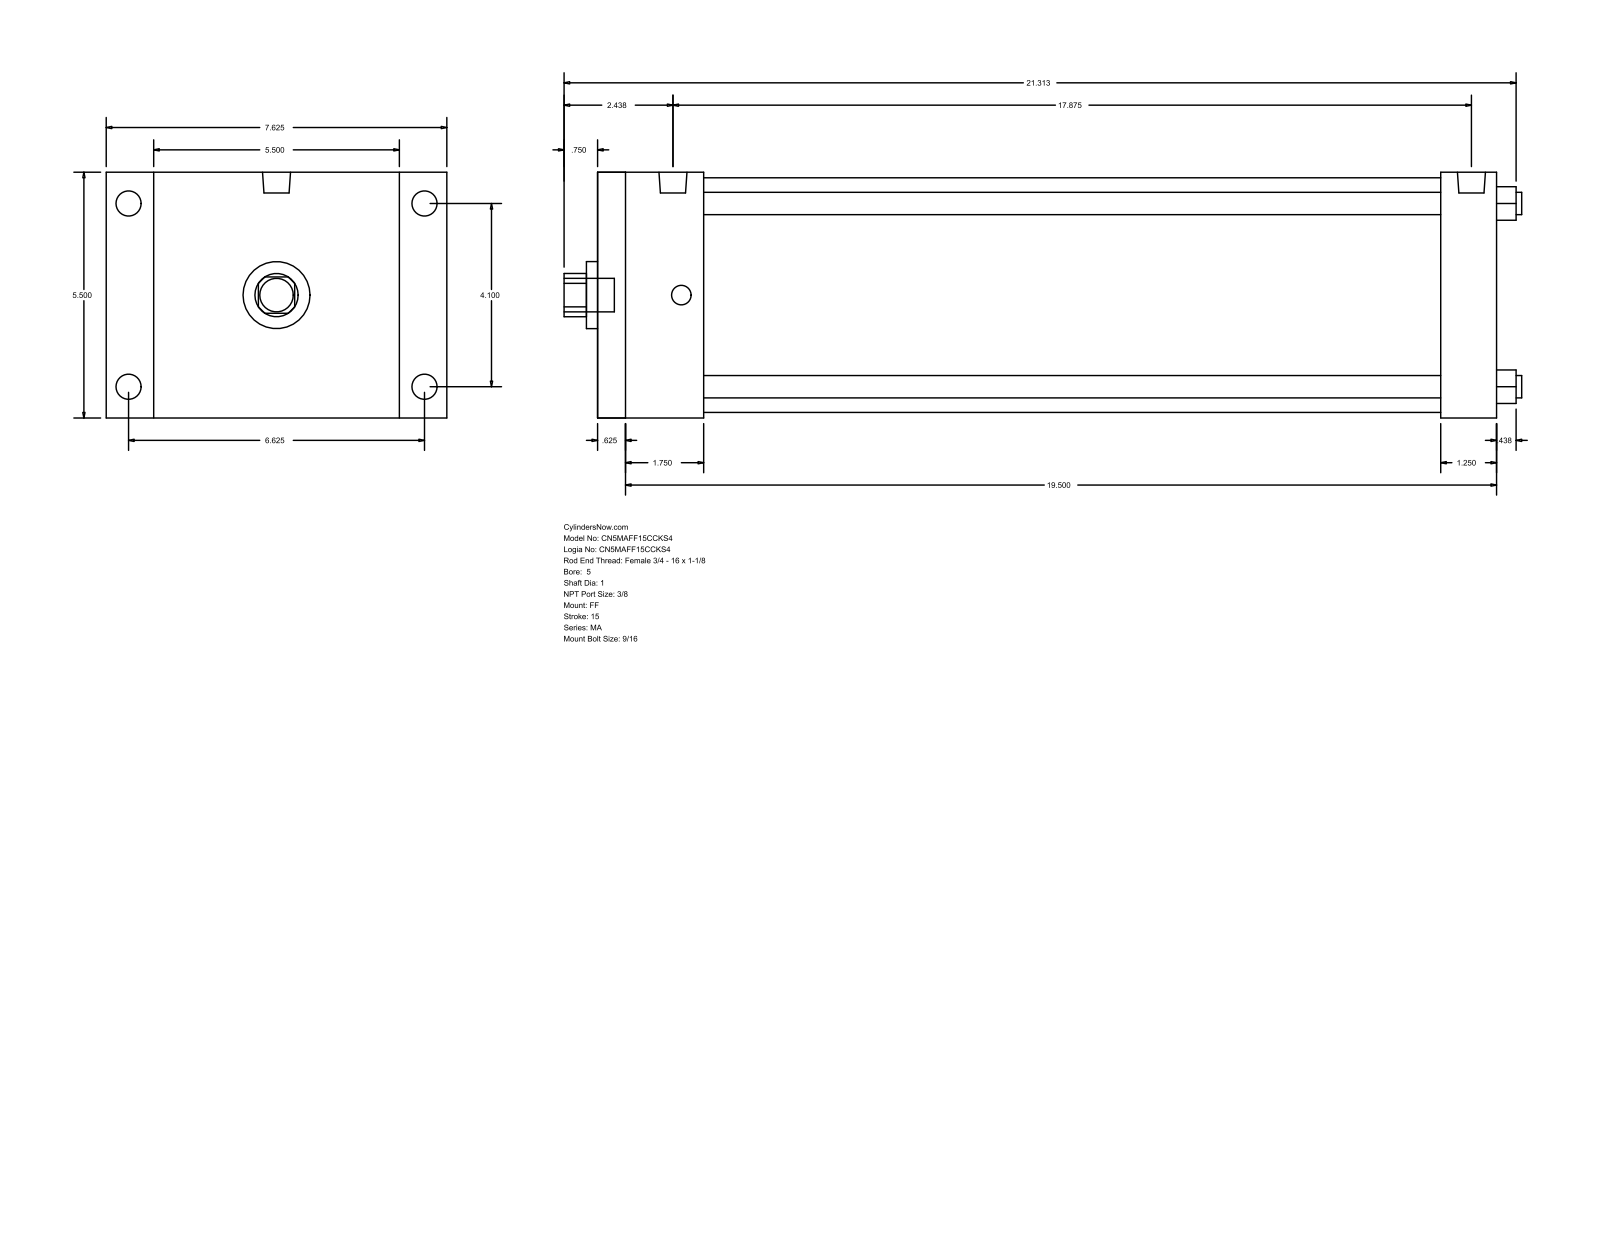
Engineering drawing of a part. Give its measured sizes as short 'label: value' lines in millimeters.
name: MA_FF__0500_1
written by: GSSL Pune (CONFIG_CONTROL_DESIGN)
unit: mm
bodies: 0 solids, 92 faces (64 planar, 28 cylindrical, 0 other)
size: 544.51 × 193.68 × 139.7
holes: 4× ⌀12.7, 1× ⌀25.4, 1× ⌀38.1, 1× ⌀133.35
bosses: 4× ⌀14.29, 4× ⌀11.11, 2× ⌀15.93, 1× ⌀19.05
rounds: 1× R12.29
face distances: 139.7, 511.18, 15.87, 495.31, 479.43, 463.56, 31.75, 60.33, 44.46, 419.1
hole spacings: 73.64, 104.14, 147.28
